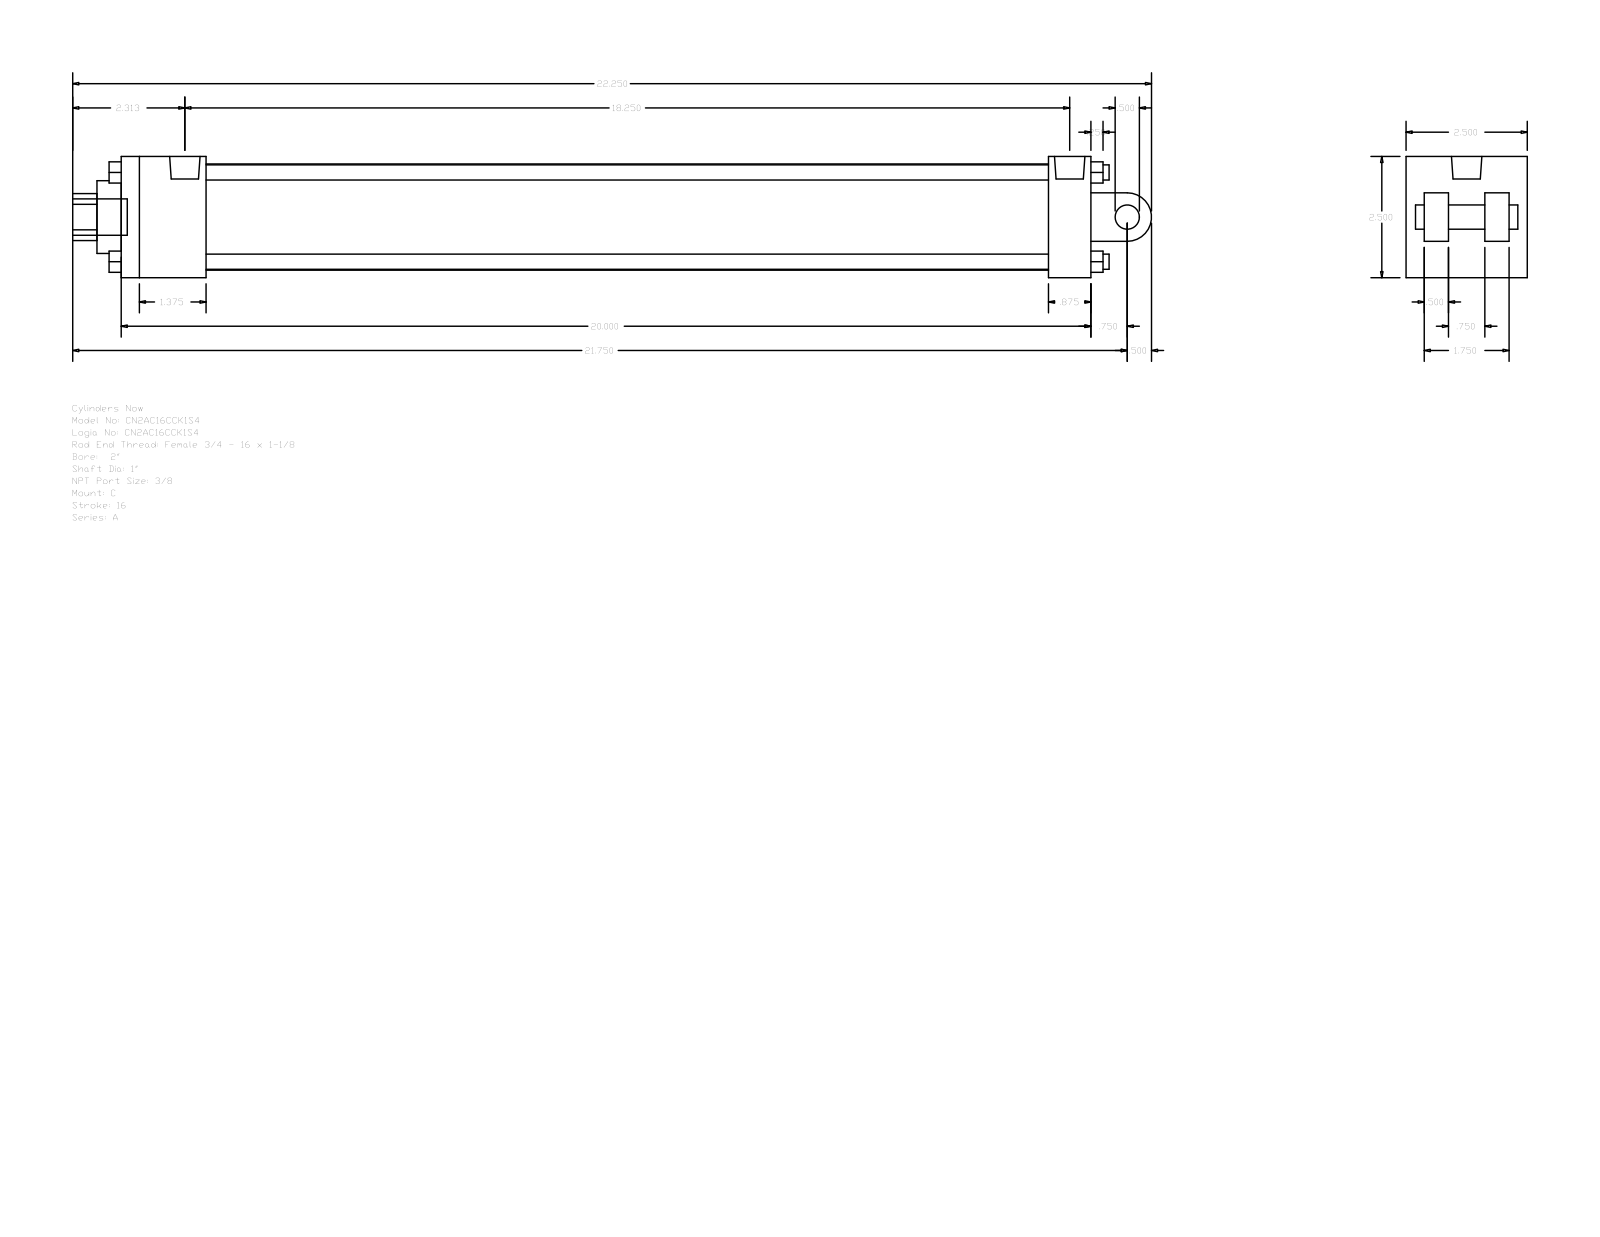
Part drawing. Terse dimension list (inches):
name: A_C__0200_1
written by: GSSL Pune (CONFIG_CONTROL_DESIGN)
unit: in
bodies: 0 solids, 135 faces (102 planar, 33 cylindrical, 0 other)
size: 22.25 × 2.5 × 2.5
holes: 2× ⌀0.219, 1× ⌀0.627, 1× ⌀1, 1× ⌀1.5, 1× ⌀2.19
bosses: 4× ⌀0.313, 2× ⌀0.219, 1× ⌀0.75, 1× ⌀0.627, 1× ⌀0.5
rounds: 1× R0.484, 1× R0.5
face distances: 2.5, 0.875, 20, 1.75, 0.5, 0.375, 1.625, 18.25, 19.125, 17.375
hole spacings: 0.157
